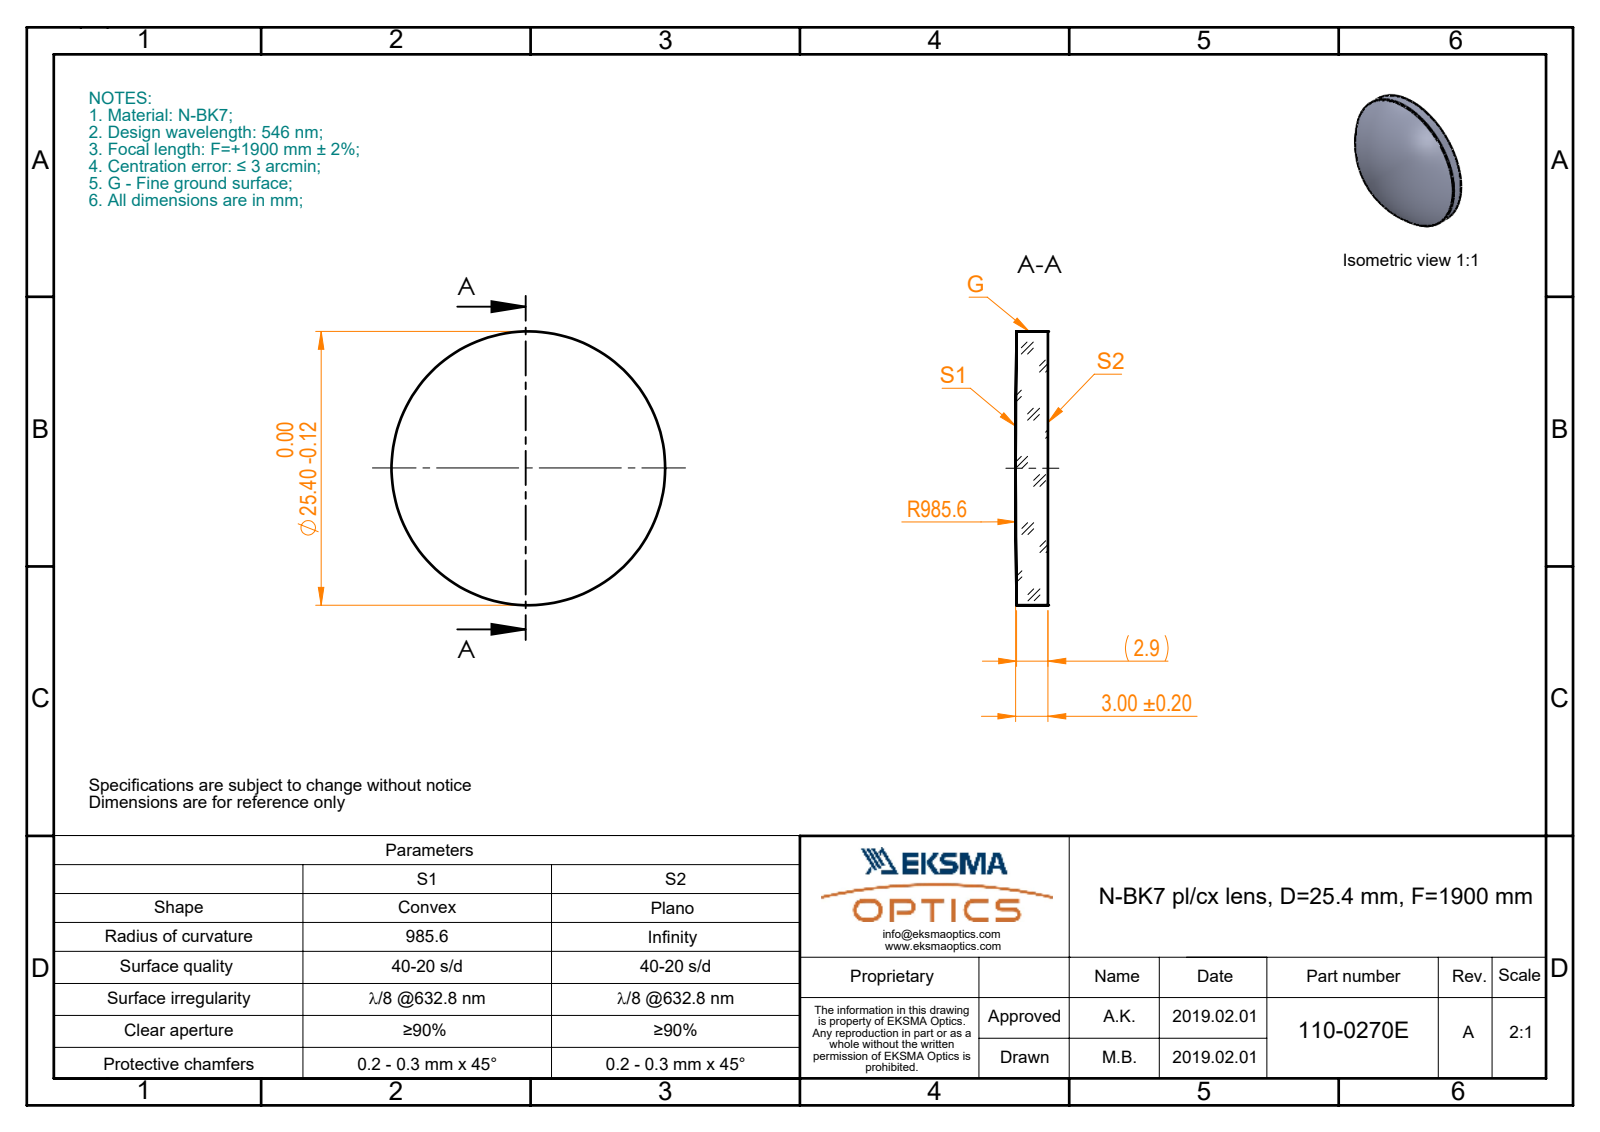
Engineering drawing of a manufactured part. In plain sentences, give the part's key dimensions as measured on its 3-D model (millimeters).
The part is named "110-0270E BK7 pl-cx 25.4 F1900". Its 3-D file was written by "SolidWorks 2017 (CONFIG_CONTROL_DESIGN)". It is 1 solid with 5 faces: 1 planar, 2 cylindrical and 2 other. Overall it measures 25.4 by 25.4 by 3 millimeters. Its volume is 1 499 cubic millimeters and its surface area 1 246 square millimeters. Round bosses or shafts: 1 of diameter 25.4.
